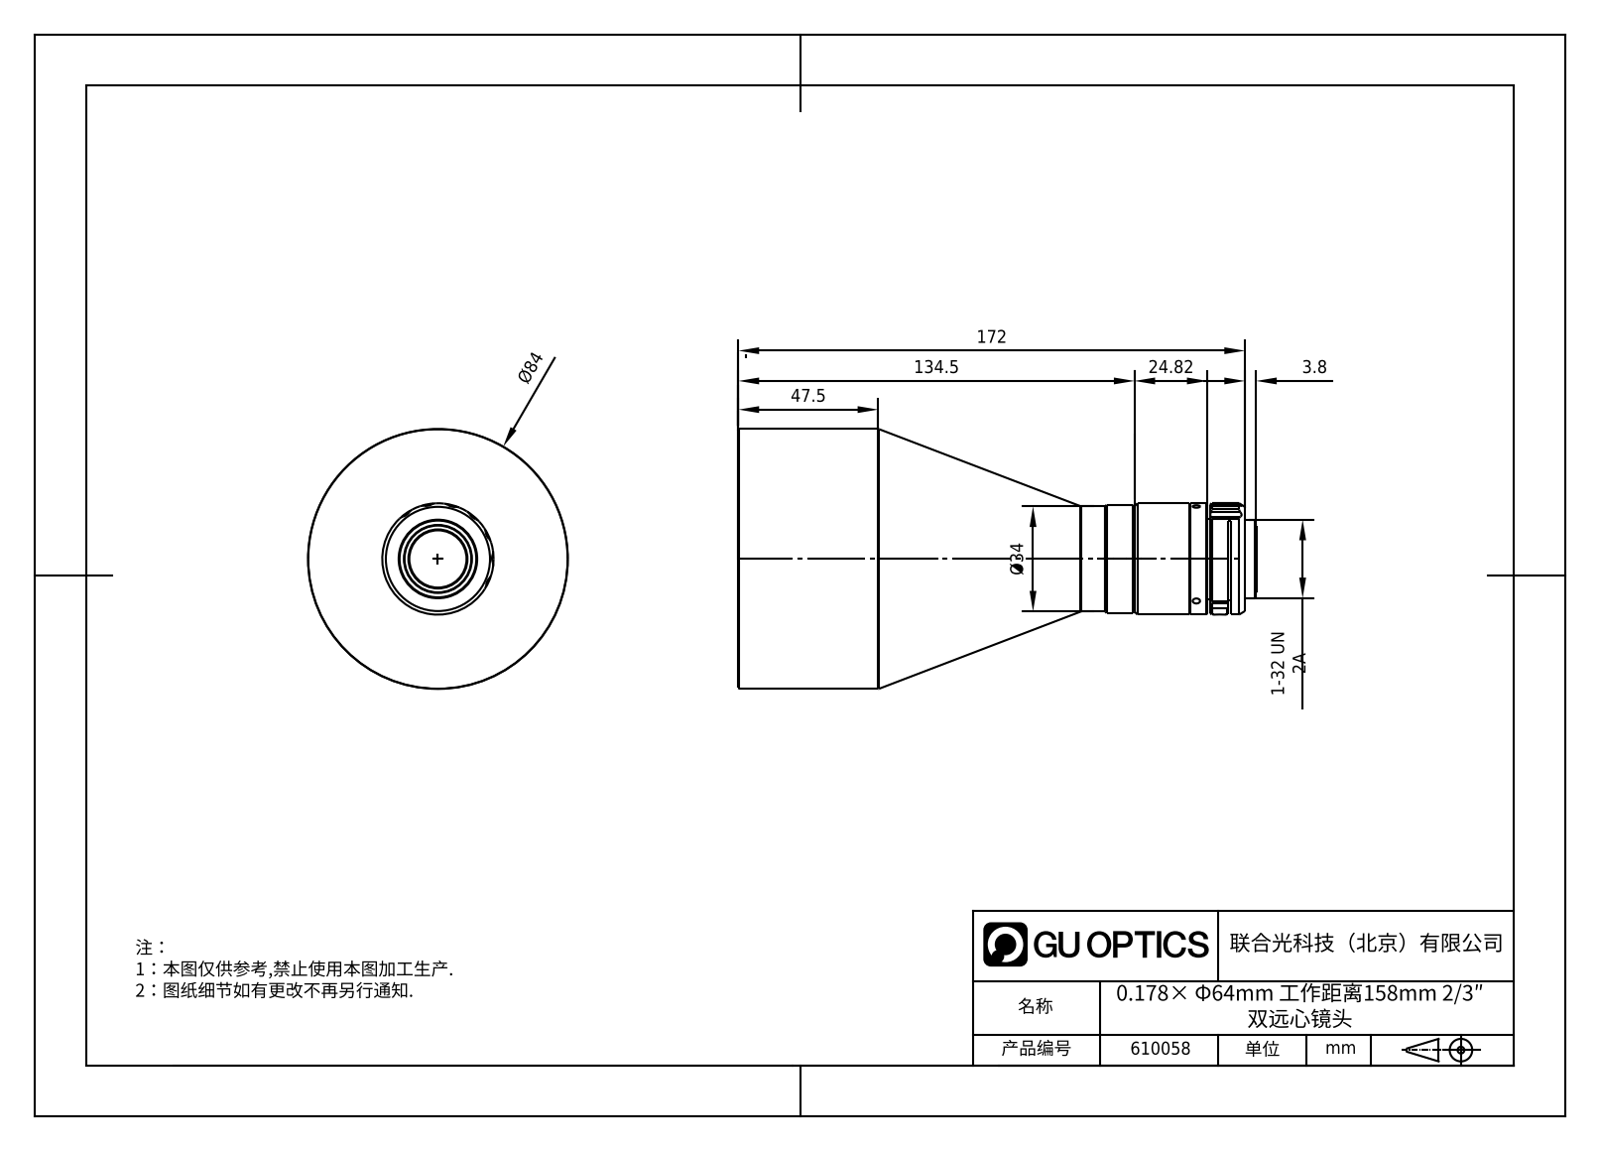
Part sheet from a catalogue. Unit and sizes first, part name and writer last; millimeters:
Units: millimetres
Overall size (bounding box): 175.92 × 84 × 84
Round holes (diameter × count): ⌀2.5 ×3, ⌀18.5 ×1, ⌀22 ×1, ⌀78.4 ×1
Round bosses / shafts (diameter × count): ⌀84 ×1, ⌀36 ×1, ⌀35 ×1, ⌀34 ×1, ⌀32.97 ×1, ⌀25.4 ×1
Partial cylindrical surfaces — rounded edges, fillets, slot ends (radius × count): R3 ×14, R4 ×7, R1.02 ×1, R1.4 ×1, R2.4 ×1
Main face-to-face distances: 172.02, 12.7, 159.32, 160.22, 0.9, 11.8, 175.82, 16.5, 15.6, 3.8
Volume: 515 304 mm³ · Surface area: 40 115 mm²
Bodies: 1 solid, 130 faces (19 planar, 69 cylindrical, 42 other)
Part name (STEP PRODUCT): DTCM230-64H-AL
STEP written by: SolidWorks 2017 (CONFIG_CONTROL_DESIGN)
